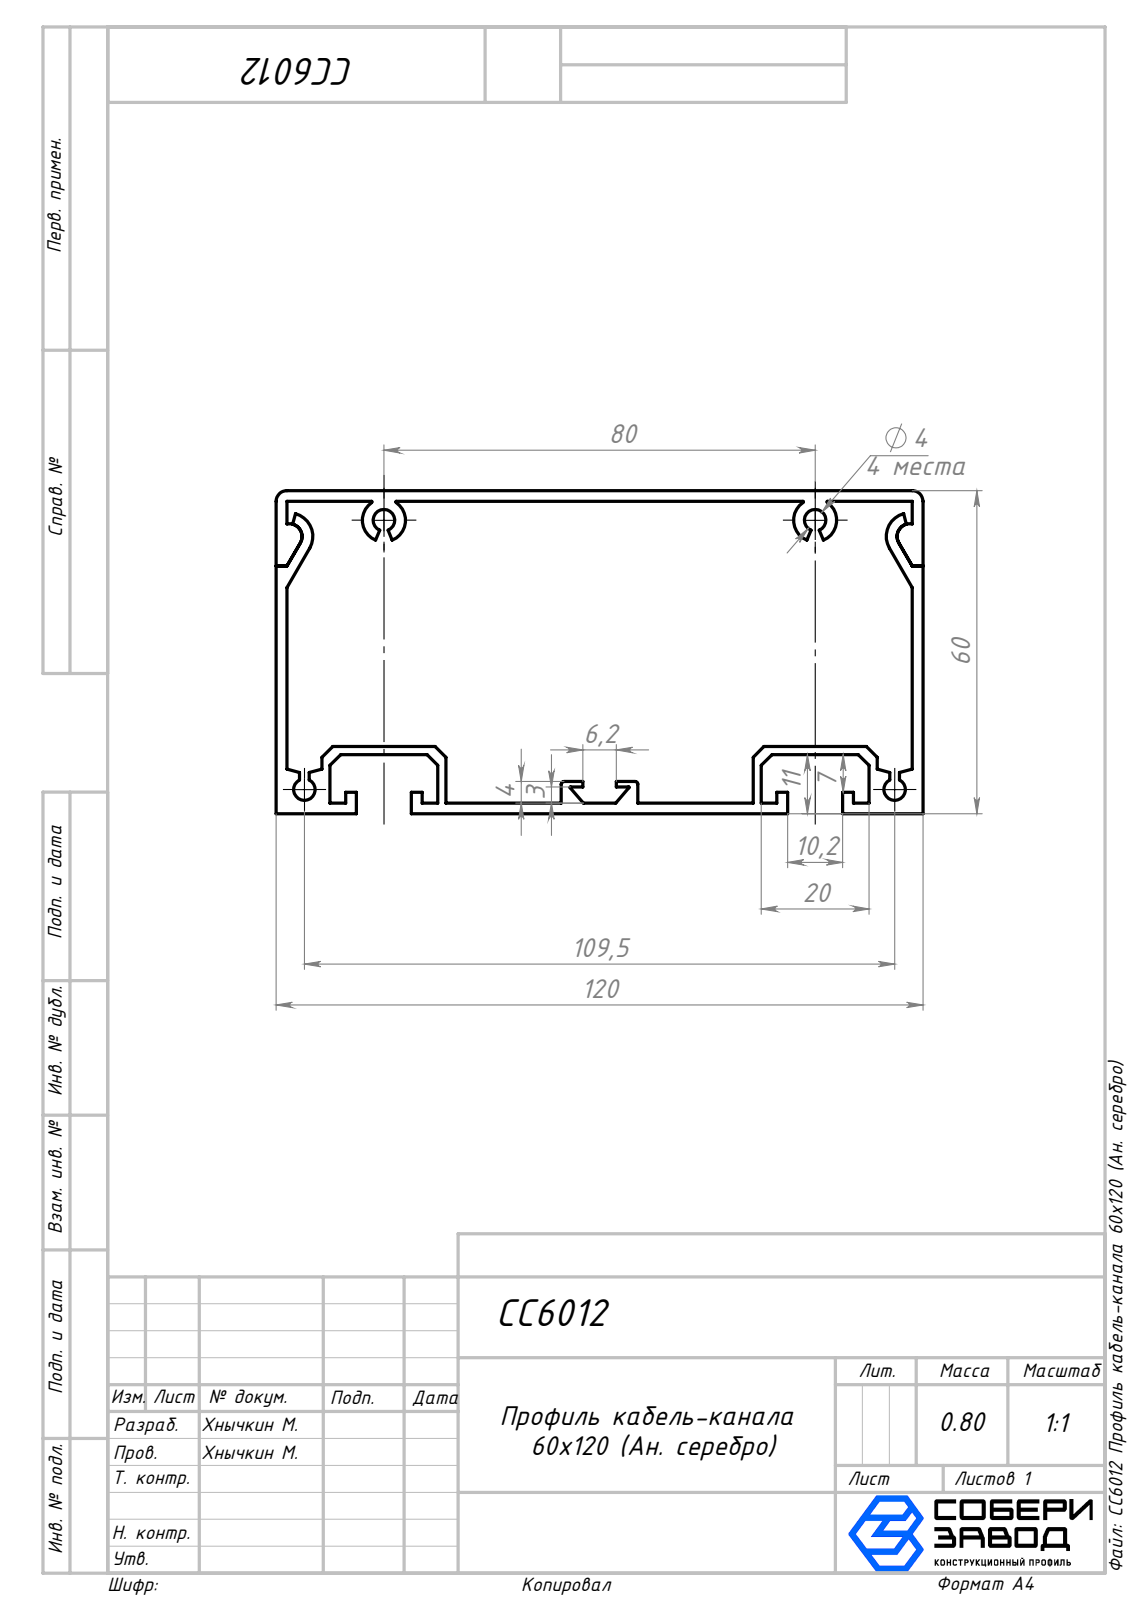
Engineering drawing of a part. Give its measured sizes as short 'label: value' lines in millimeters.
name: CC6012 Профиль кабель-канала 60х120 (Ан. серебро); Алюм. кабель, крышка 60х120_00; Алюм. кабель 60х120_00
written by: SolidWorks 2026 (AUTOMOTIVE_DESIGN)
unit: mm
bodies: 2 solids, 130 faces (96 planar, 34 cylindrical, 0 other)
size: 120 × 100 × 60
volume: 101 543 mm³; area: 99 161 mm²
holes: 4× ⌀4
rounds: 2× R0.1, 2× R0.5, 2× R2, 2× R2.35, 2× R4, 2× R4.35
face distances: 2, 58, 60, 118, 56, 120, 1.5, 12.5, 10.5, 45.5
hole spacings: 52.13, 107.13, 80, 109.5
